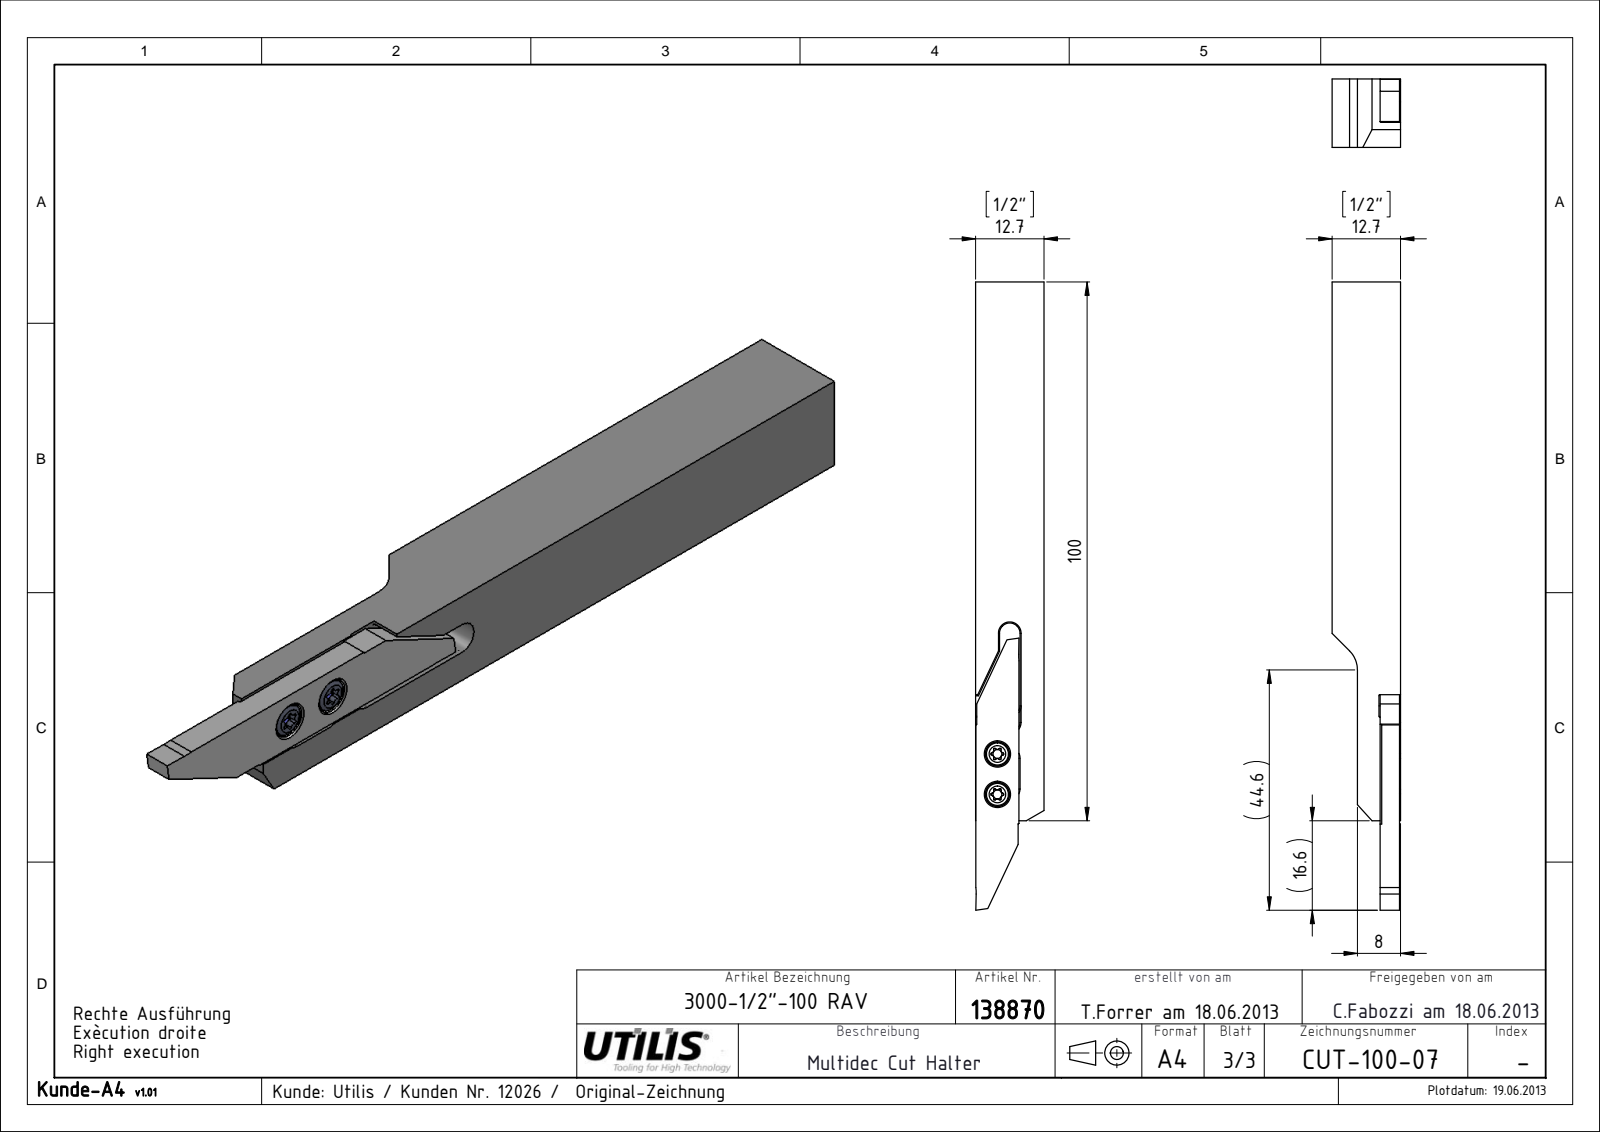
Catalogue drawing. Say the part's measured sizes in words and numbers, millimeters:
The part is named "MSP-16_M3x7.3 T08; CUT-100-07; CUT-100-Kunde_3000-1-2-100 RAV; CUT- 3000 R+L Lang NUR FÜR KUNDEN _L-Lang". Its 3-D file was written by "SolidWorks 2014 (CONFIG_CONTROL_DESIGN)". It is 4 solids with 118 faces: 34 planar, 56 cylindrical and 28 other. Overall it measures 116.6 by 12.7 by 12.7 millimeters. Its volume is 14 247 cubic millimeters and its surface area 6 428 square millimeters. Round holes: 2 of diameter 2.5, 2 of diameter 4.9. Round bosses or shafts: 2 of diameter 4.1, 2 of diameter 3. Partial cylindrical surfaces (rounded edges, fillets, slot ends): 12 of radius 0.2, 12 of radius 0.45, 4 of radius 2.1, 2 of radius 10, 1 of radius 5. The main face-to-face distances are 12.7, 3.8, 8.9, 8, 4.2, 4.7, 12.5, 7.8, 3.6, 4.65. The hole center spacings are 3.75, 7.5, 3.65, 3.85, 7.4, 7.6.
